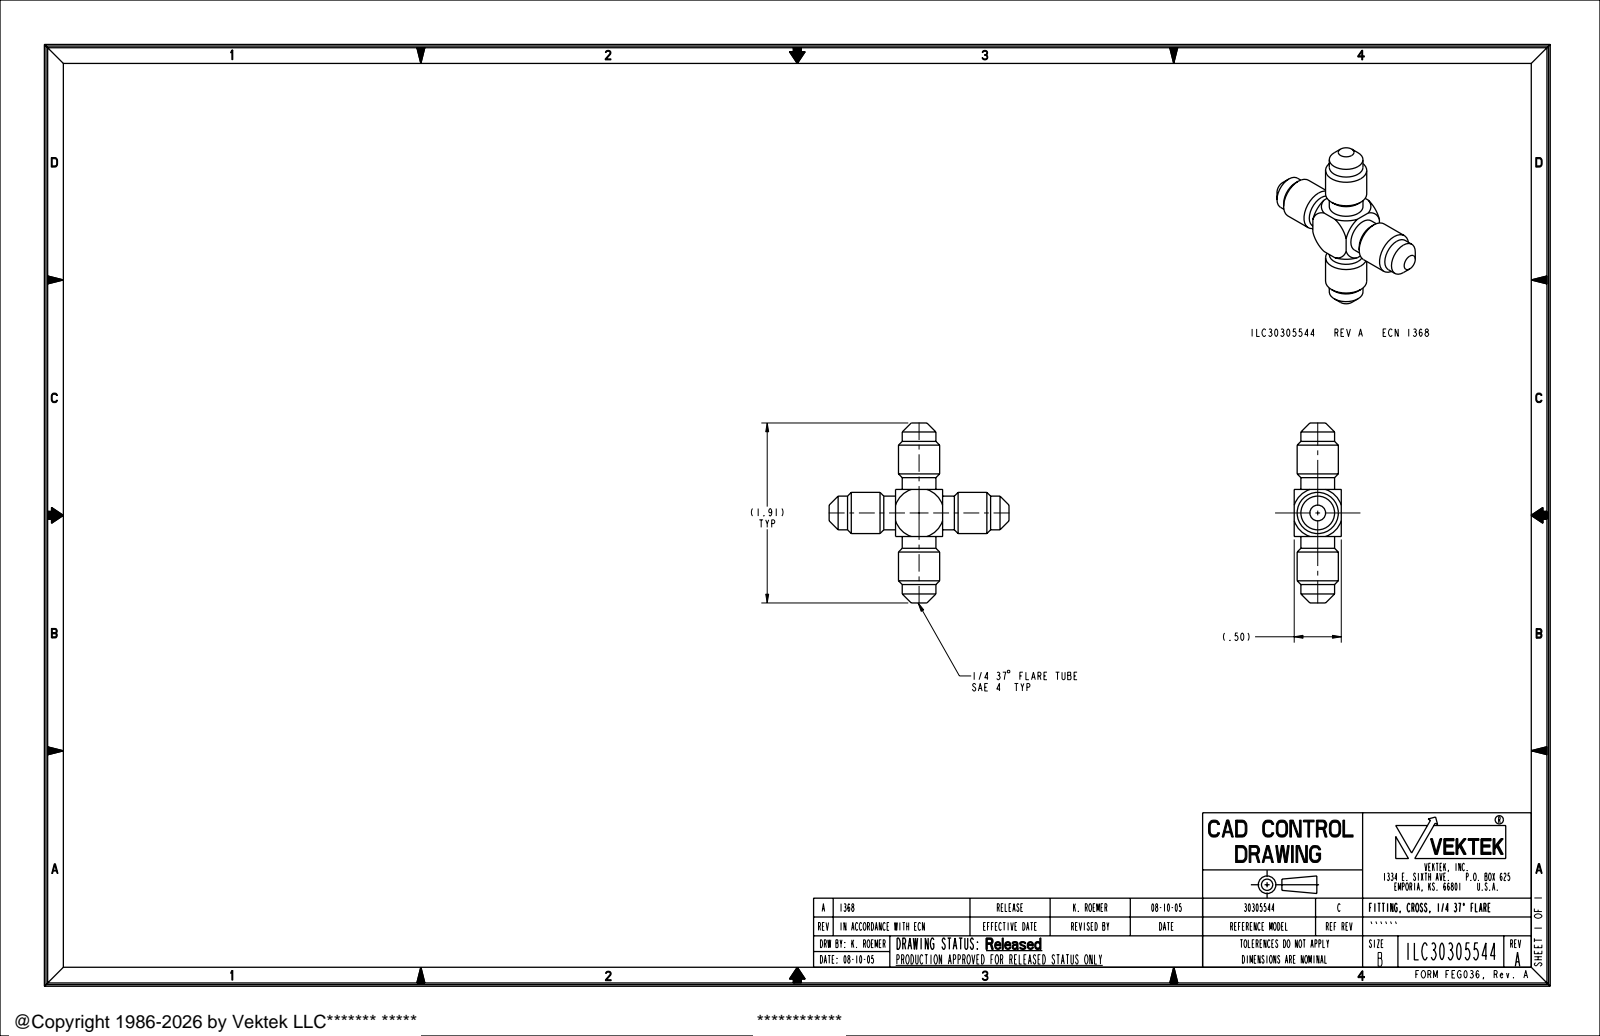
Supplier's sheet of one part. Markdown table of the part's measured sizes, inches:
| quantity | value |
| --- | --- |
| part name | ILC30305544 |
| STEP written by | PRO/ENGINEER BY PARAMETRIC TECHNOLOGY CORPORATION, 2004290 (AUTOMOTIVE_DESIGN_CC2) |
| units | inches |
| bodies | 1 solid, 70 faces (6 planar, 32 cylindrical, 32 other) |
| overall size | 1.911 × 1.911 × 0.5 |
| volume | 0.377 in³ |
| surface area | 6.595 in² |
| round holes (diameter × count) | 0.167 × 2 |
| round bosses / shafts (diameter × count) | 0.437 × 2, 0.358 × 2 |
| main face-to-face distances | 0.5 |
